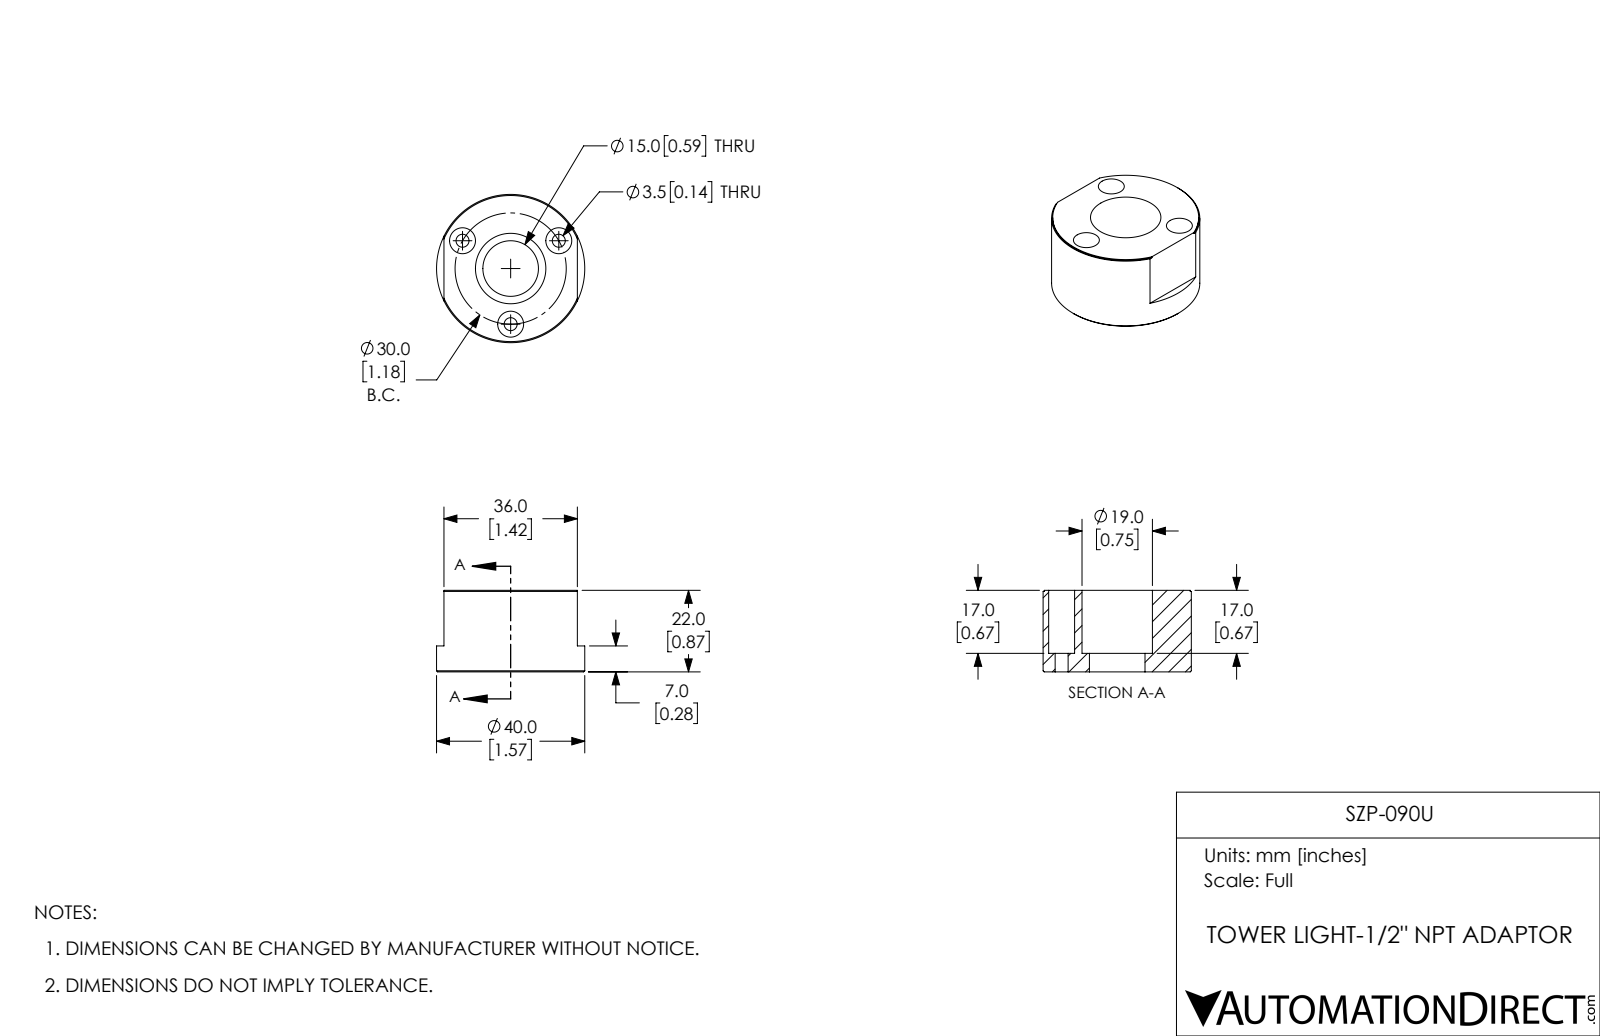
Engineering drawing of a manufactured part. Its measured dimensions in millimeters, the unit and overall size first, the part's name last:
Units: millimetres
Overall size (bounding box): 40 × 40 × 22
Round holes (diameter × count): ⌀3.5 ×3, ⌀7 ×3, ⌀15 ×1, ⌀19 ×1
Round bosses / shafts (diameter × count): ⌀40 ×1
Partial cylindrical surfaces — rounded edges, fillets, slot ends (radius × count): R19.7 ×1
Main face-to-face distances: 22, 36, 17, 5, 15, 2, 7, 14.7, 16.7, 21.7
Hole centre spacings: 15, 26
Volume: 19 120 mm³ · Surface area: 7 361 mm²
Bodies: 1 solid, 34 faces (12 planar, 20 cylindrical, 2 other)
Part name (STEP PRODUCT): SZP-090U
STEP written by: SolidWorks 2017 (AUTOMOTIVE_DESIGN)
